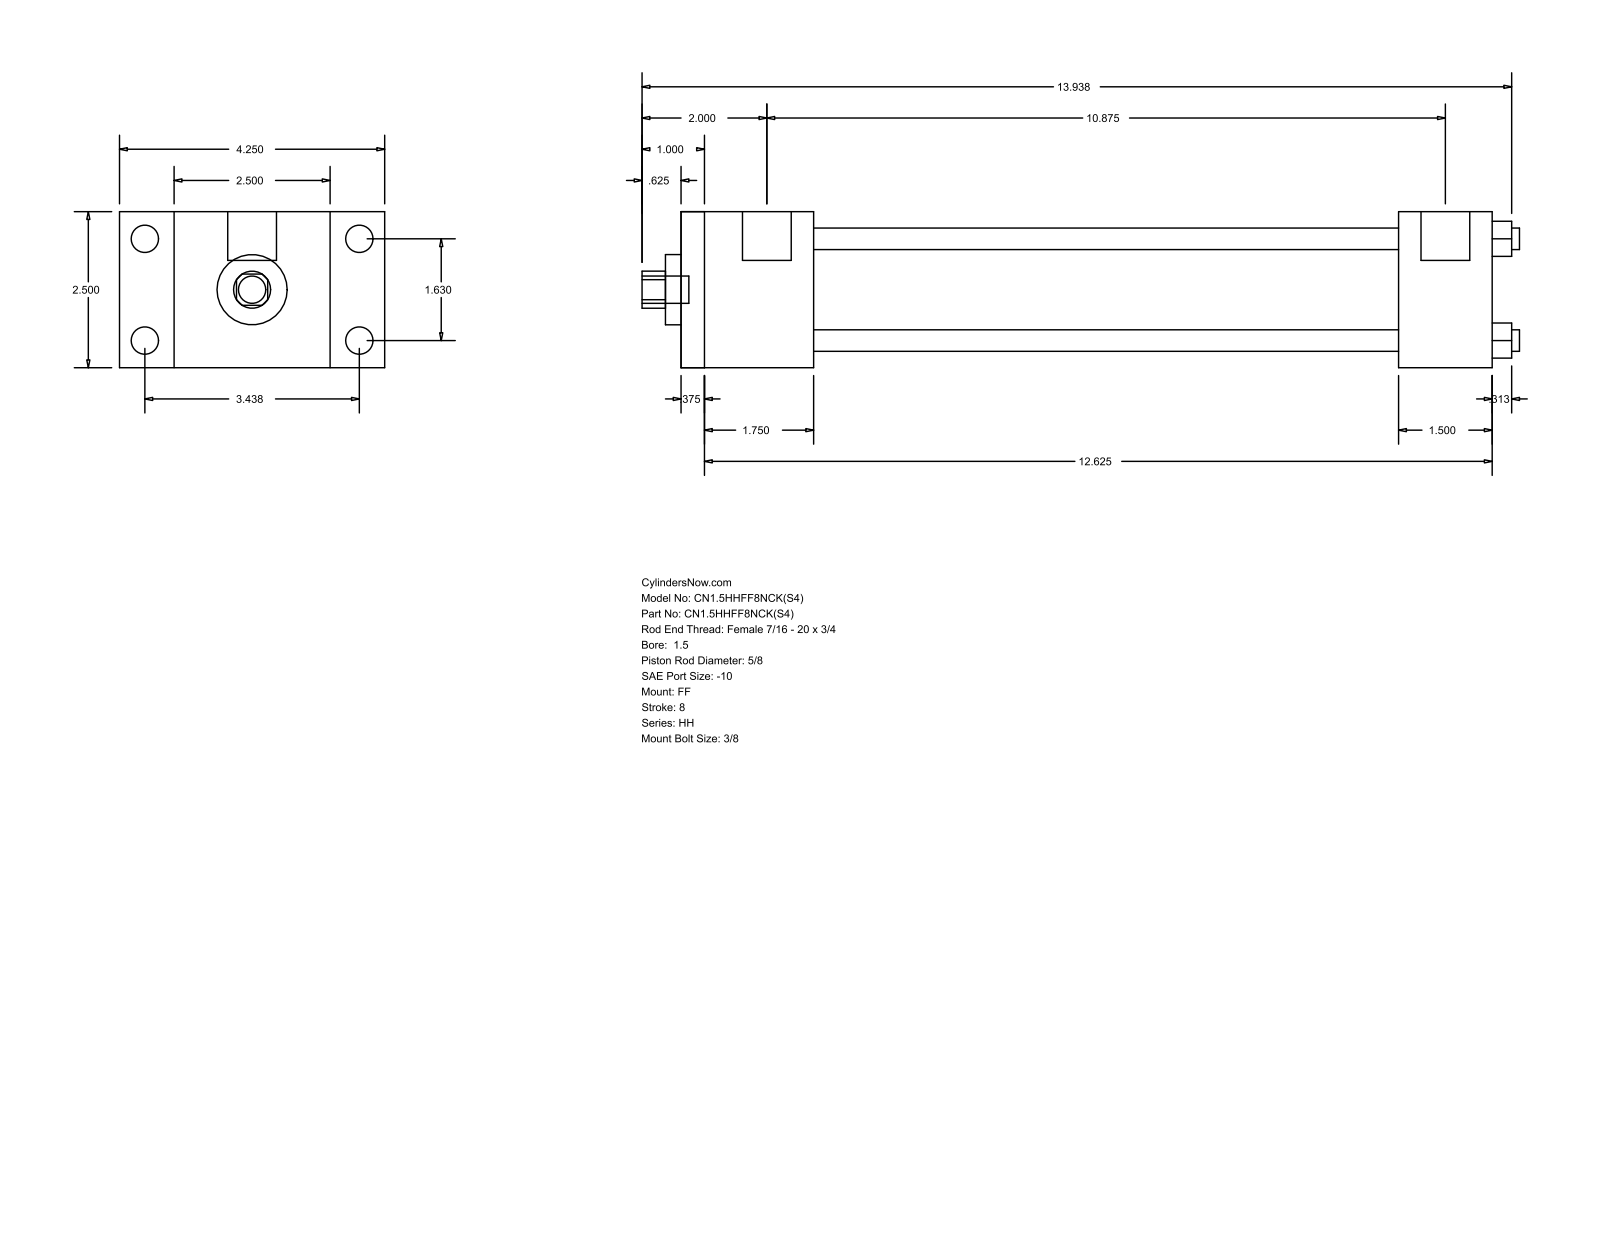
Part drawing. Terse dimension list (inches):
name: HH_FF__0150_0.625
written by: GSSL Pune (CONFIG_CONTROL_DESIGN)
unit: in
bodies: 0 solids, 92 faces (64 planar, 28 cylindrical, 0 other)
size: 14.063 × 4.25 × 2.5
holes: 4× ⌀0.345, 1× ⌀0.625, 1× ⌀1.125, 1× ⌀1.75
bosses: 4× ⌀0.438, 4× ⌀0.219, 2× ⌀0.781, 1× ⌀0.437
rounds: 1× R0.297
face distances: 2.5, 13, 0.375, 12.625, 2.125, 1.75, 10.875, 11.5, 11.125, 9.375
hole spacings: 1.152, 1.63, 2.305
